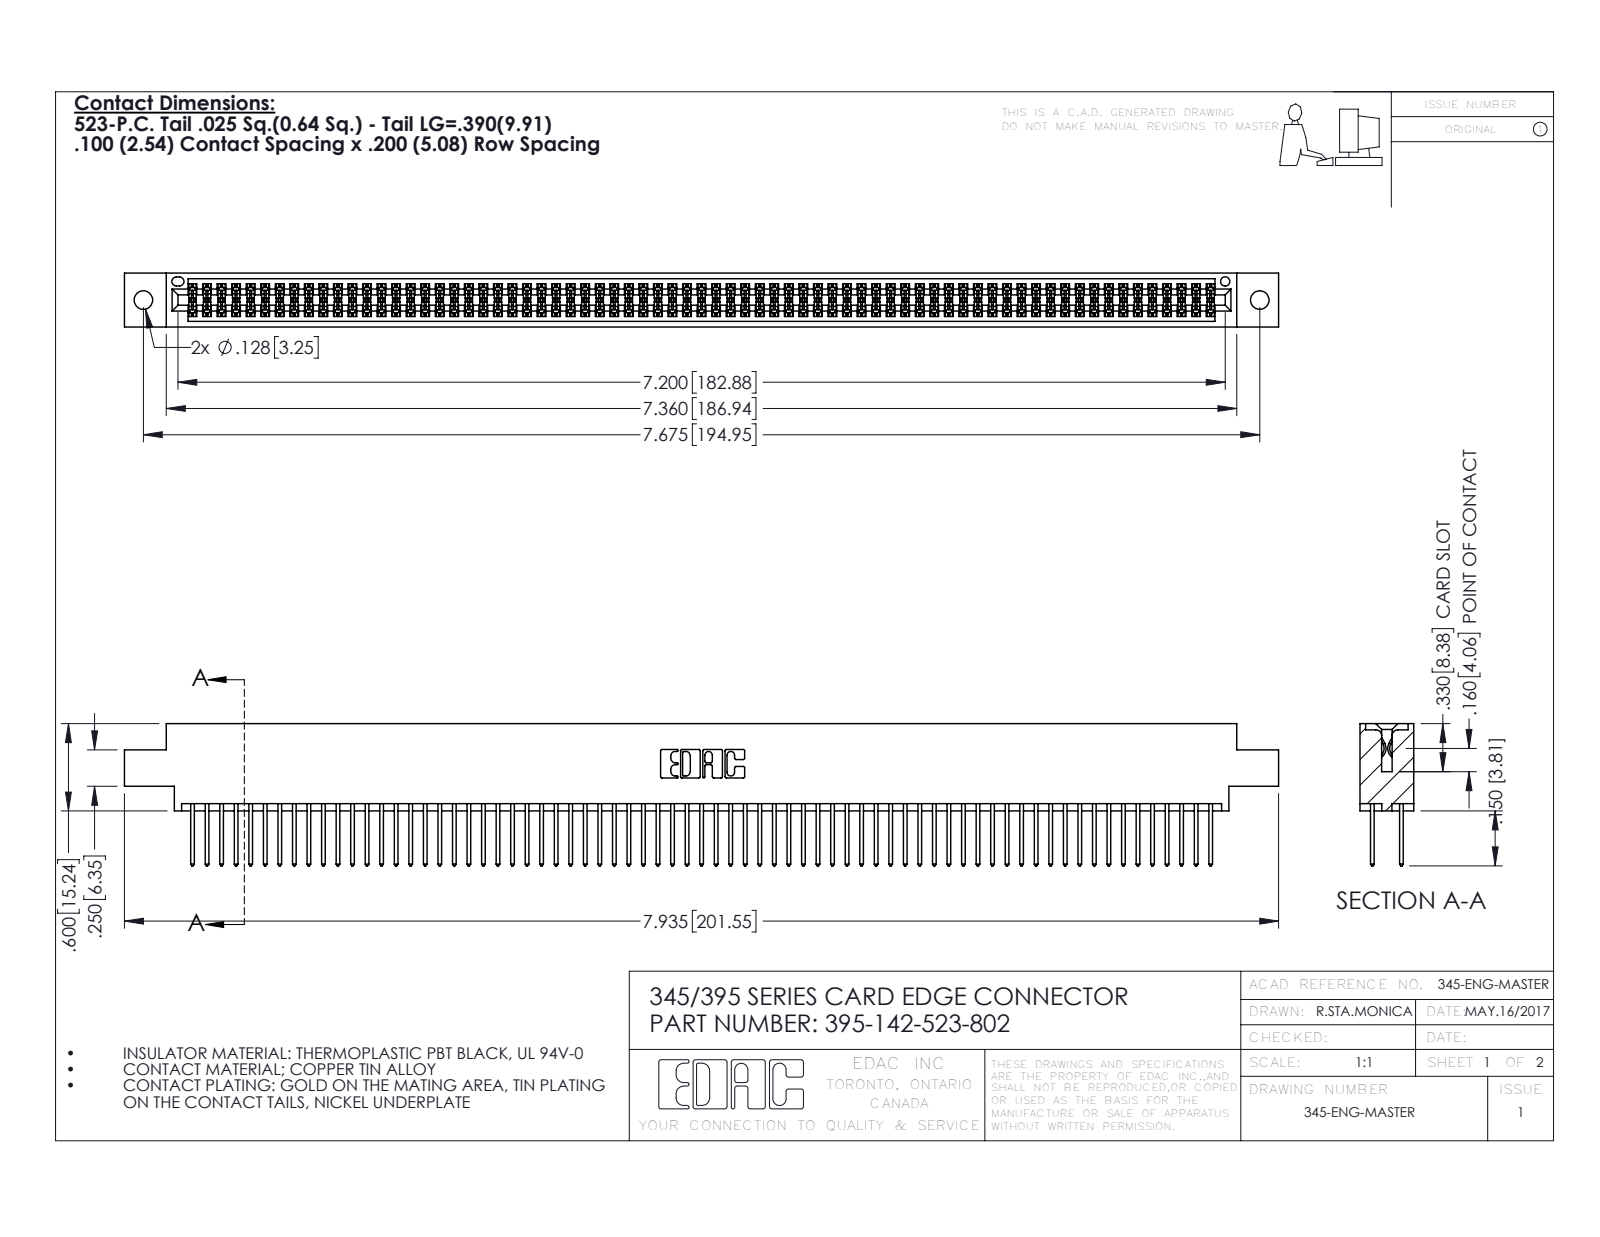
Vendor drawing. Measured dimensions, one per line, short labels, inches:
name: 395-142-523-802; 345 Part_0.170 Offset - 0.128 Dia; 345-292-001_345-293-123
written by: SolidWorks 2016 (CONFIG_CONTROL_DESIGN)
unit: in
bodies: 143 solids, 7230 faces (4770 planar, 2460 cylindrical, 0 other)
size: 7.935 × 0.977 × 0.37
volume: 1.22 in³; area: 48.49 in²
holes: 2× ⌀0.128, 1× ⌀0.064
rounds: 213× R0.006, 142× R0.01, 22× R0.01, 6× R0.007, 6× R0.031, 3× R0.026, 2× R0.014, 2× R0.019
face distances: 0.072, 0.298, 0.2, 0.098, 0.272, 0.025, 0.37, 0.225, 0.175, 0.149
hole spacings: 0.27, 7.439, 7.675
